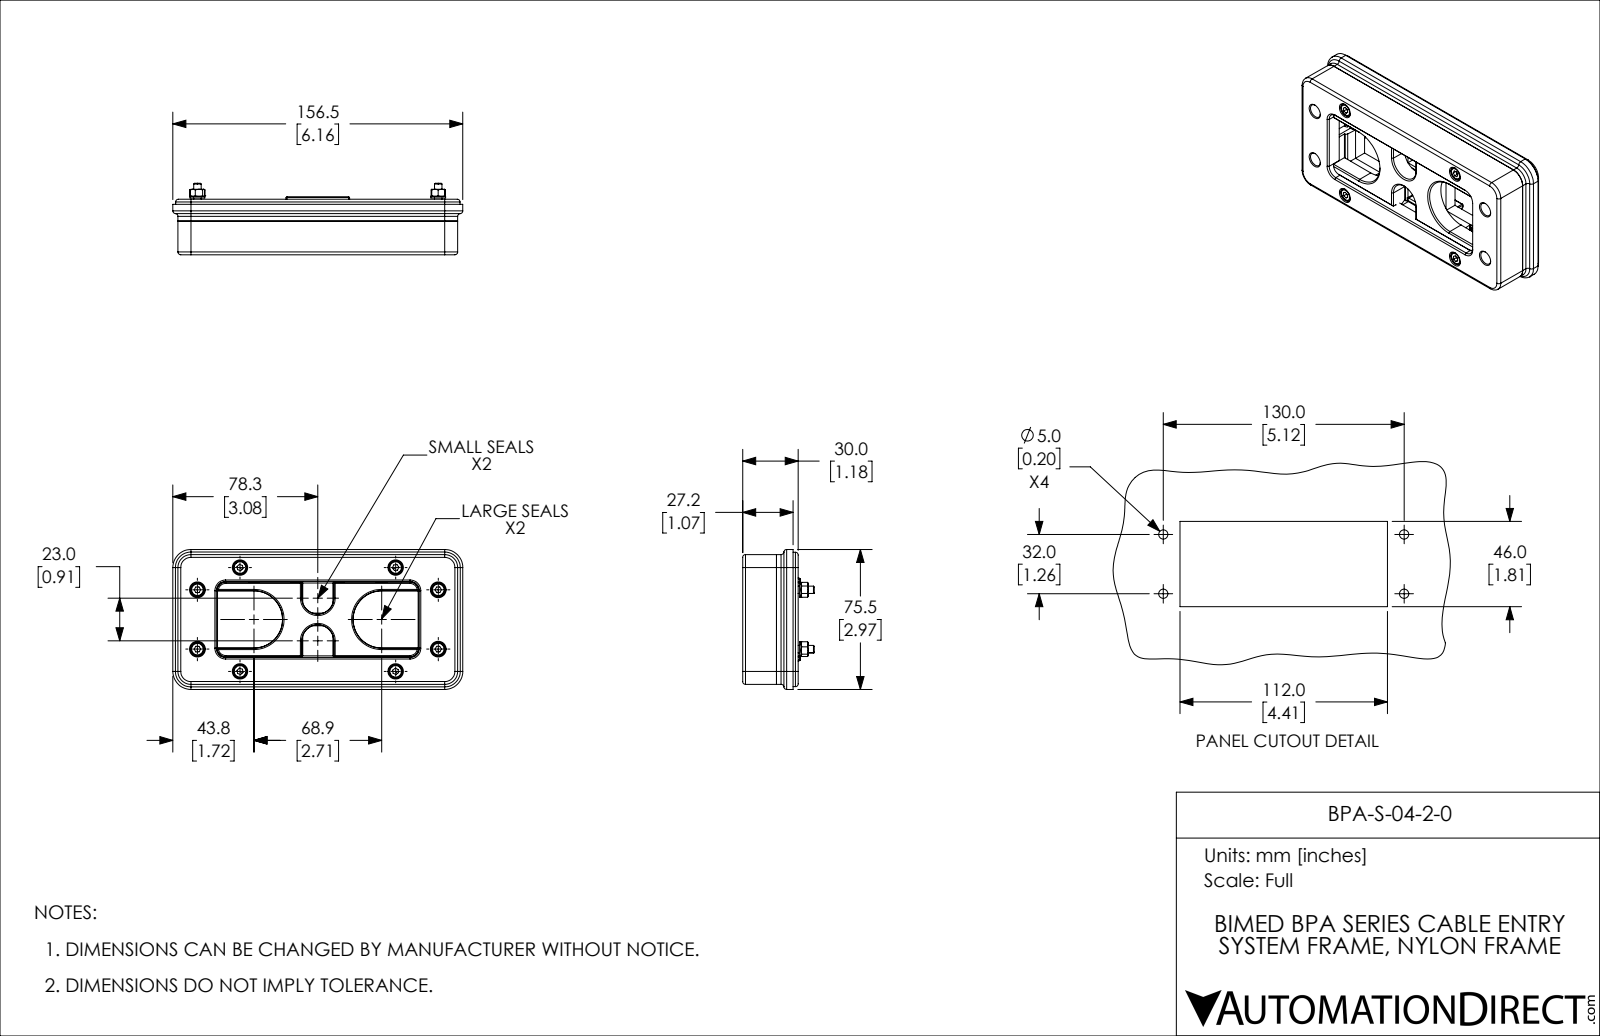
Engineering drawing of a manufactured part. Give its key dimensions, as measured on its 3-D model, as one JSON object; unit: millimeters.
{"part_name": "BPA-S-04-2-0", "step_written_by": "SolidWorks 2021 (CONFIG_CONTROL_DESIGN)", "units": "millimeters", "bodies": {"solids": 29, "faces": 1745, "planar": 865, "cylindrical": 522, "other": 358}, "overall_size": [156.5, 75.5, 38.6], "volume_mm3": 181127, "surface_area_mm2": 94500, "round_holes": [[3.24, 8], [4.5, 8], [4.3, 4], [5, 4], [7.3, 4], [7.5, 4], [8, 4]], "round_bosses_or_shafts": [[7, 8], [4, 8], [8.1, 4], [8, 4], [6.9, 4]], "partial_cylinders_radius": [[0.5, 51], [1, 32], [1.5, 20], [0.4, 10], [0.75, 4], [3.4, 4], [3.5, 4], [4, 4]], "face_to_face_distances": [2.25, 2.5, 67.75, 27.2, 18.8, 8.4, 3, 9.6, 3.5, 67.5], "hole_center_spacings": [25.94, 49.65, 107.67, 115.69, 32, 56, 84, 100.96]}
